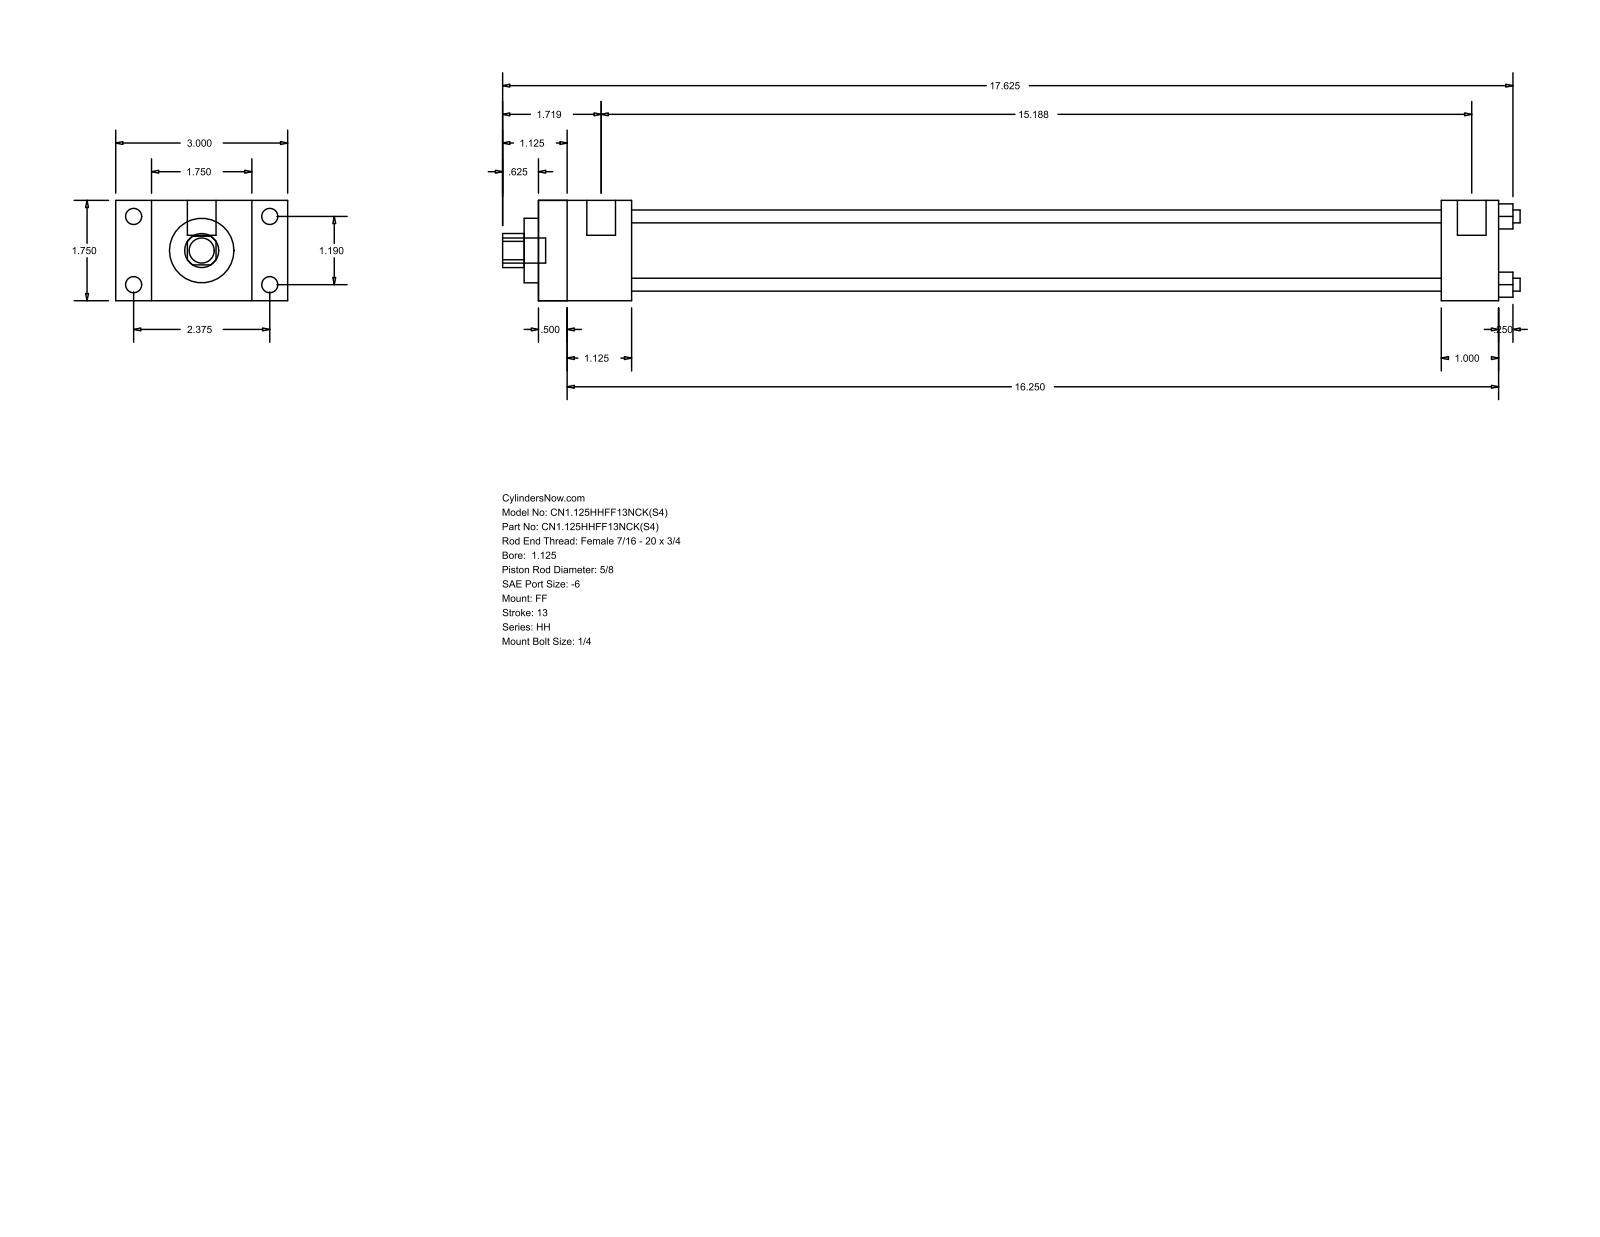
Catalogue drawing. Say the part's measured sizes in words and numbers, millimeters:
The part is named "HH_FF__0112_0.625". Its 3-D file was written by "GSSL Pune (CONFIG_CONTROL_DESIGN)". It is 0 solids with 92 faces: 64 planar, 28 cylindrical and 0 other. Overall it measures 450.85 by 76.2 by 44.45 millimeters. Round holes: 4 of diameter 5.71, 1 of diameter 15.88, 1 of diameter 28.57, 1 of diameter 34.92. Round bosses or shafts: 4 of diameter 7.14, 4 of diameter 5.56, 2 of diameter 12.7, 1 of diameter 11.11. Partial cylindrical surfaces (rounded edges, fillets, slot ends): 1 of radius 7.54. The main face-to-face distances are 44.46, 425.44, 15.87, 12.69, 412.75, 60.33, 28.58, 41.27, 400.05, 387.36. The hole center spacings are 21.37, 30.22, 42.74.
